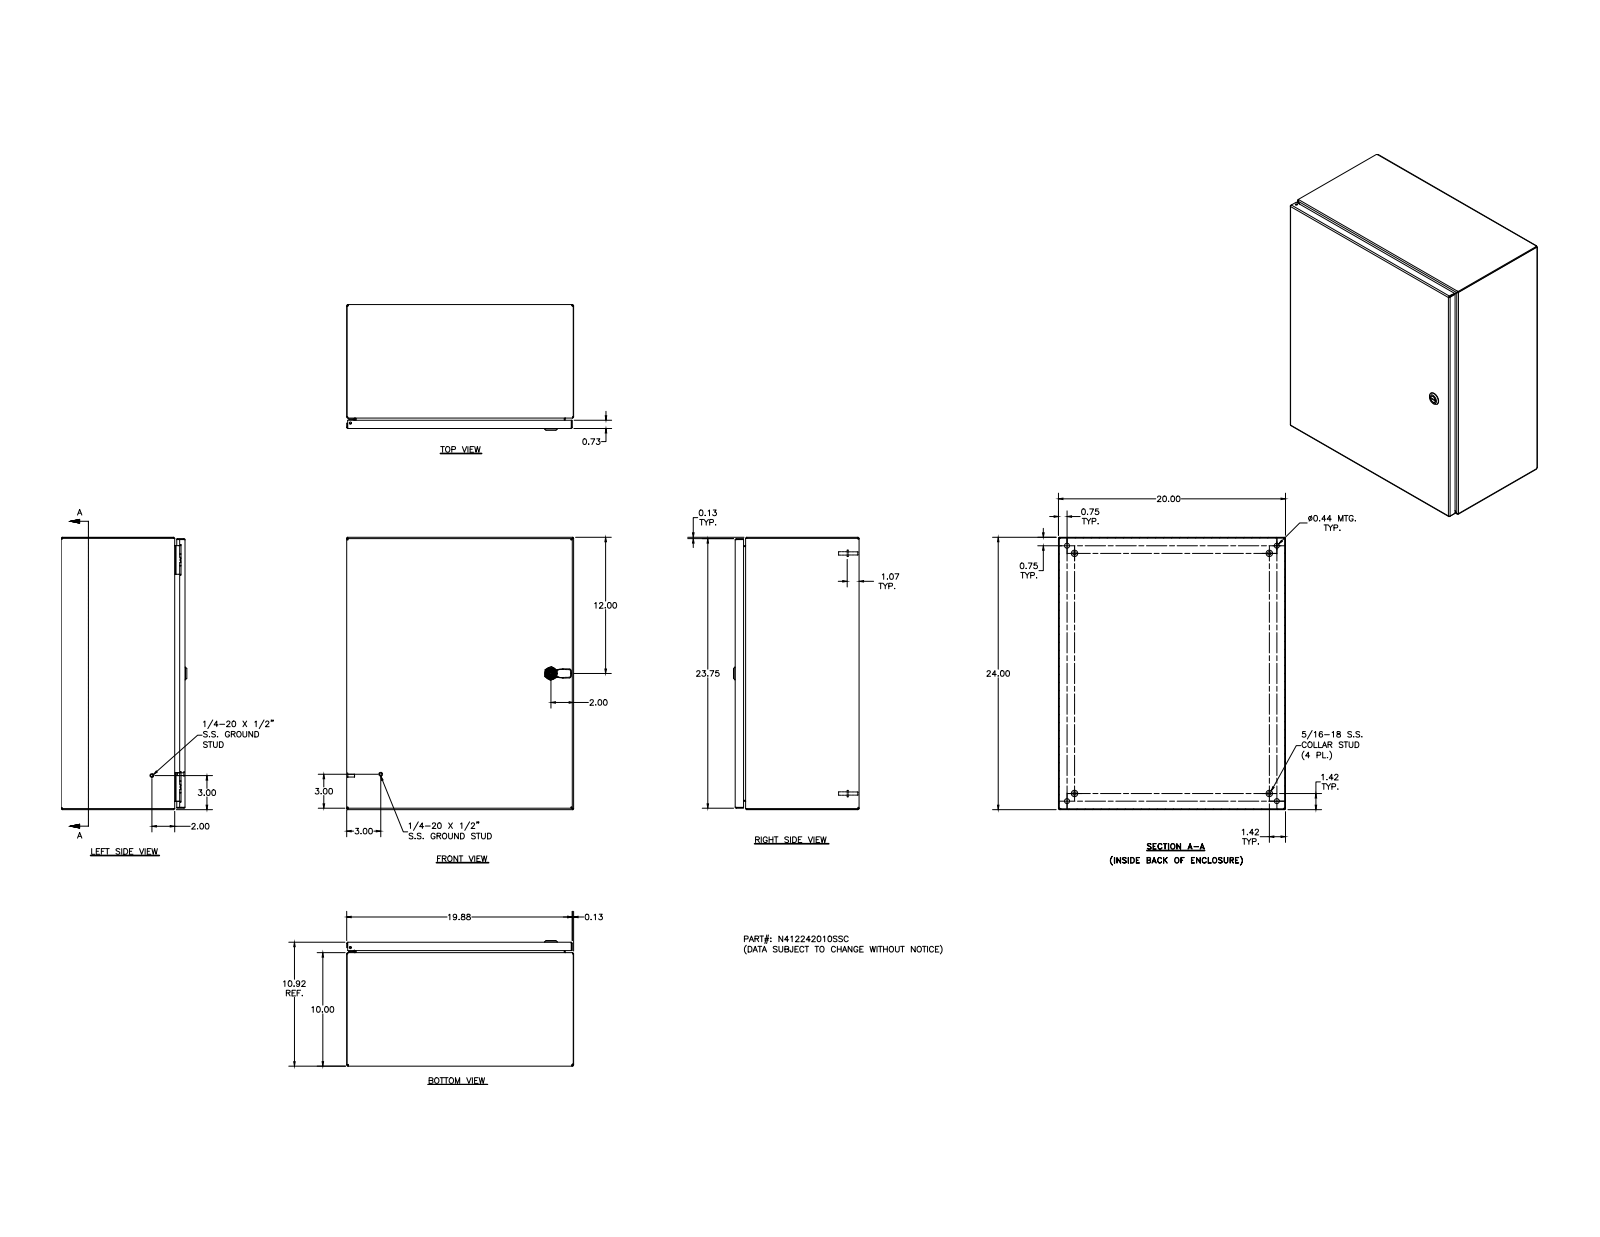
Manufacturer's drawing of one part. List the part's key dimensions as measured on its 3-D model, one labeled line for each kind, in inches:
Part name (STEP PRODUCT): N412242010SSC; N412242010SSCBKP; 388151; N4122420SSCLID (+8 more)
STEP written by: Autodesk Inventor 2011 (AUTOMOTIVE_DESIGN)
Units: inches
Bodies: 34 solids, 1384 faces (531 planar, 509 cylindrical, 344 other)
Overall size (bounding box): 24 × 20 × 11.075
Volume: 149.2 in³ · Surface area: 4 054 in²
Round holes (diameter × count): ⌀0.188 ×5, ⌀0.093 ×4, ⌀0.152 ×4, ⌀0.167 ×4, ⌀0.172 ×4, ⌀0.437 ×4, ⌀0.156 ×2, ⌀0.187 ×1, ⌀0.197 ×1, ⌀0.315 ×1, ⌀0.394 ×1, ⌀0.402 ×1
Round bosses / shafts (diameter × count): ⌀0.25 ×10, ⌀0.563 ×4, ⌀0.36 ×4, ⌀0.32 ×4, ⌀0.3 ×4, ⌀0.275 ×4, ⌀0.256 ×4, ⌀0.164 ×4
Partial cylindrical surfaces — rounded edges, fillets, slot ends (radius × count): R0.031 ×30, R0.05 ×26, R0.105 ×20, R0.016 ×18, R0.125 ×14, R0.02 ×9, R0.032 ×8, R0.07 ×8
Main face-to-face distances: 0.074, 10.843, 19.926, 10.769, 10.917, 23.926, 20, 19.852, 24, 23.852
Hole centre spacings: 20, 0.017, 0.66, 18.872, 0.019, 0.5, 0.648, 0.652
